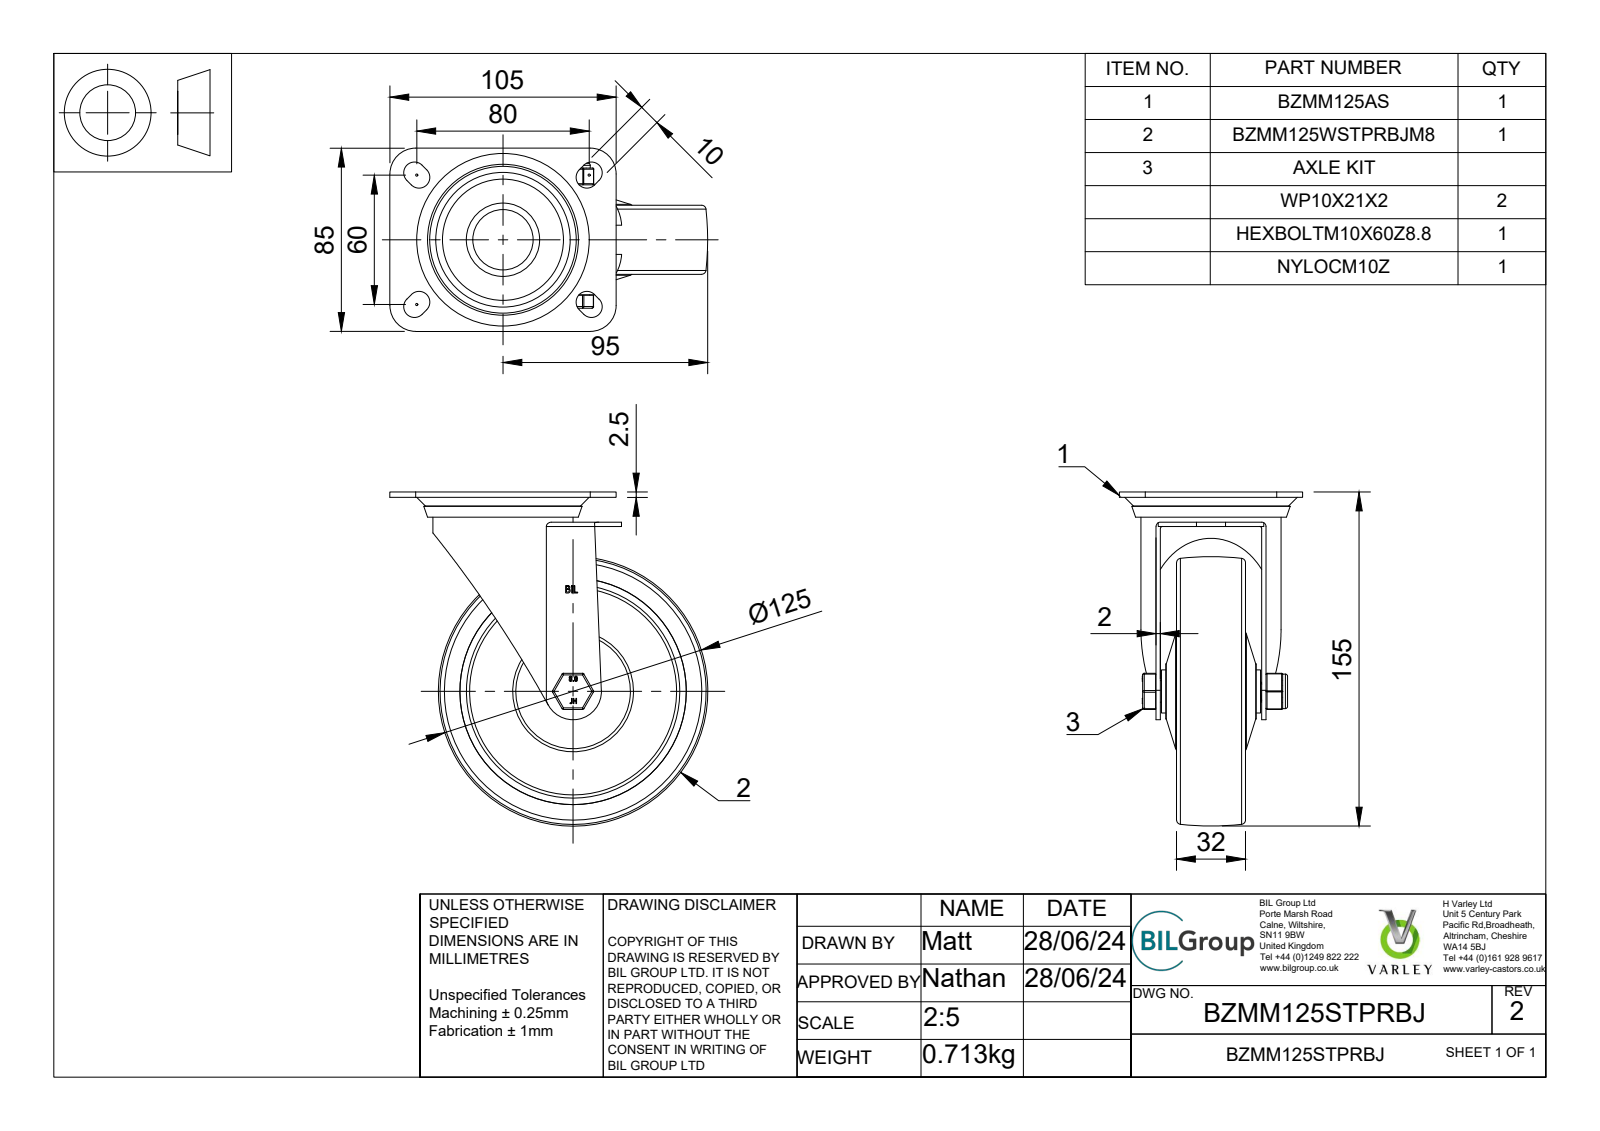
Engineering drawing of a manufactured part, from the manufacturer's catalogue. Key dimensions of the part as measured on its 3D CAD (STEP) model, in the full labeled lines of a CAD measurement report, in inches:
Part name (STEP PRODUCT): BZMM125STPRBJ - 2 v4; BZMM125AS - 2 - 47 v1; ZINC PLATED, PRESSED STEEL TOP PLATE; ZINC PLATED, PRESSED STEEL FORKS (+8 more)
STEP written by: Autodesk Translation Framework v13.14.0.145 (AUTOMOTIVE_DESIGN)
Units: inches
Bodies: 25 solids, 743 faces (281 planar, 183 cylindrical, 279 other)
Overall size (bounding box): 6.102 × 5.807 × 3.346
Volume: 17.26 in³ · Surface area: 245 in²
Round holes (diameter × count): ⌀0.394 ×1, ⌀0.406 ×1, ⌀0.409 ×1, ⌀0.423 ×1, ⌀0.472 ×1, ⌀0.886 ×1, ⌀1.102 ×1, ⌀1.181 ×1, ⌀1.22 ×1, ⌀1.26 ×1, ⌀1.28 ×1, ⌀1.378 ×1
Round bosses / shafts (diameter × count): ⌀2.559 ×1, ⌀2.205 ×1, ⌀1.929 ×1, ⌀1.752 ×1, ⌀1.535 ×1, ⌀1.358 ×1, ⌀1.339 ×1, ⌀1.201 ×1
Partial cylindrical surfaces — rounded edges, fillets, slot ends (radius × count): R0.02 ×18, R0.03 ×12, R0.197 ×8, R0.472 ×5, R0.039 ×4, R0.079 ×2, R0.815 ×2, R0.517 ×1
Main face-to-face distances: 0.177, 0.079, 0.541, 0.295, 0.374, 0.719, 0.098, 0.197, 1.014, 0.915
